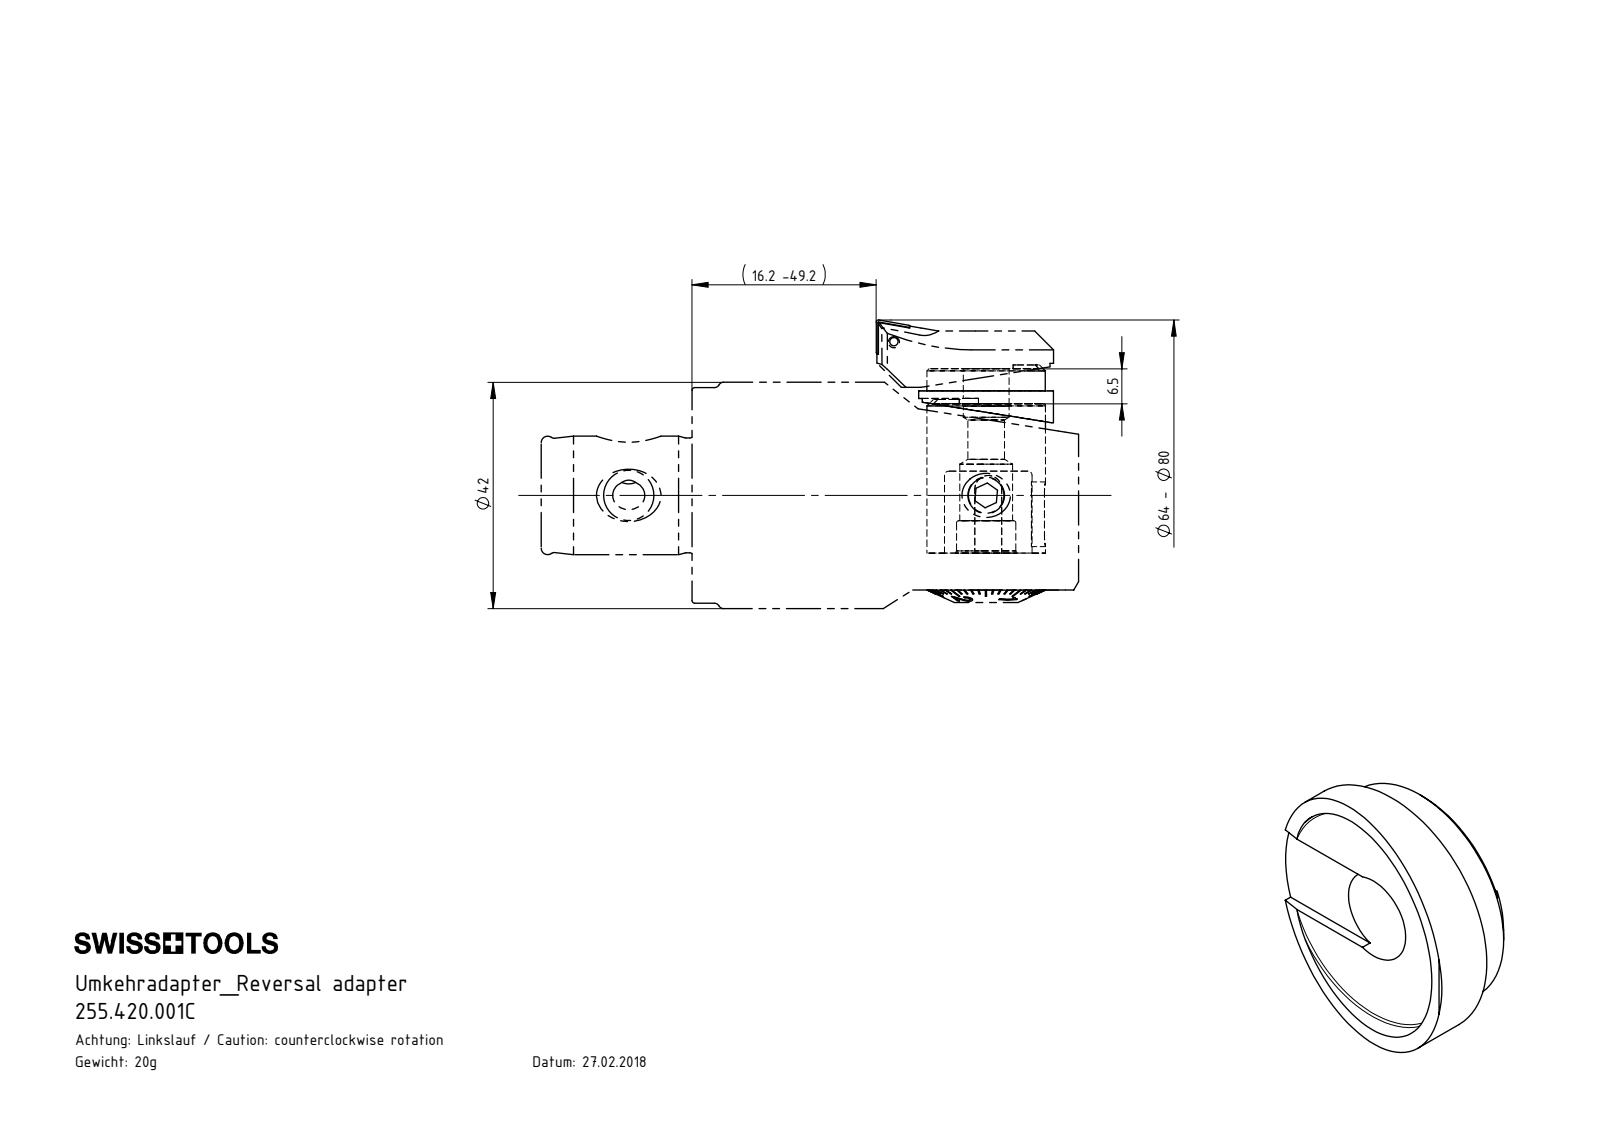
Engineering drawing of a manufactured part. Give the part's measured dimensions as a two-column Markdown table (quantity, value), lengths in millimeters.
| quantity | value |
| --- | --- |
| part name | F42-U00.001.006_B; 255.420.001C |
| STEP written by | SolidWorks 2017 (CONFIG_CONTROL_DESIGN) |
| units | millimeters |
| bodies | 1 solid, 28 faces (12 planar, 11 cylindrical, 5 other) |
| overall size | 25 × 25 × 10.7 |
| volume | 2 498 mm³ |
| surface area | 1 746 mm² |
| round holes (diameter × count) | 8.5 × 1, 22 × 1 |
| round bosses / shafts (diameter × count) | 25 × 1 |
| partial cylindrical surfaces (radius × count) | 0.5 × 2 |
| main face-to-face distances | 6.5, 4.1, 2.4, 5.5, 1.4, 1, 0.7, 4.8, 6.2, 7.2 |
